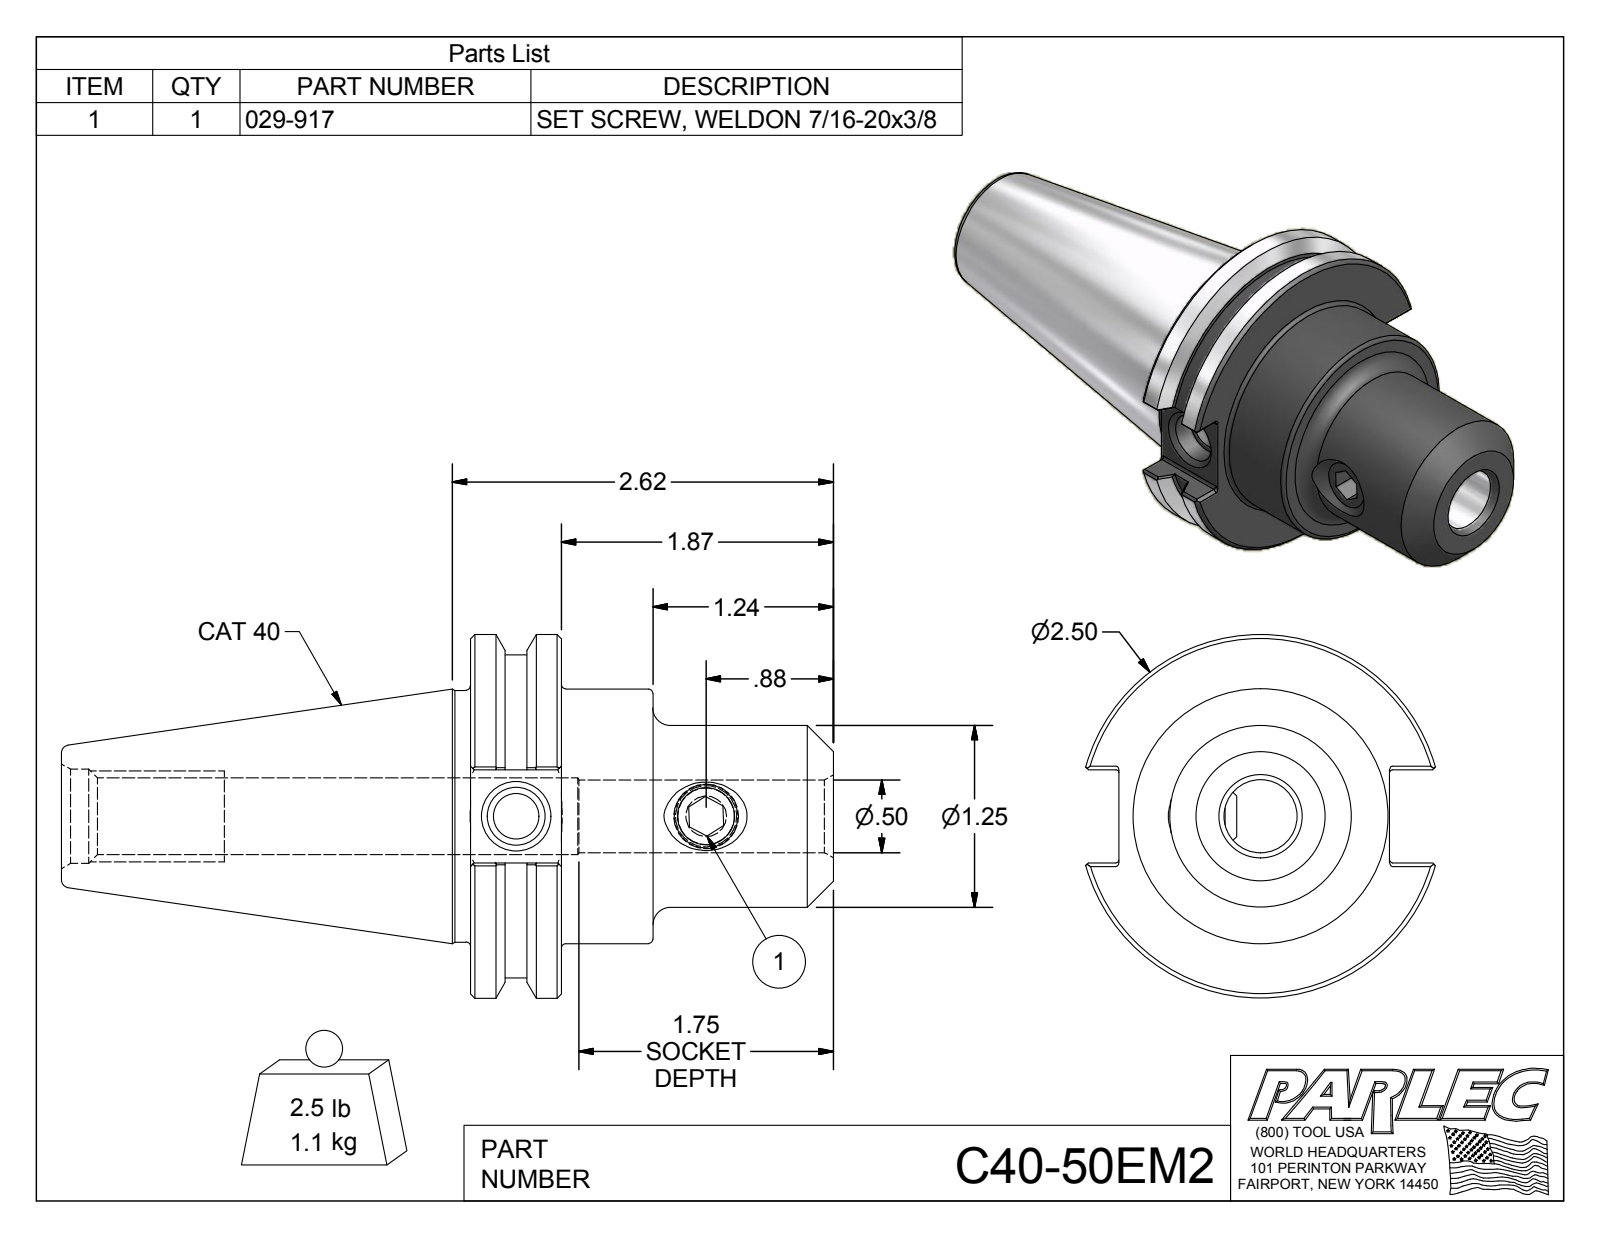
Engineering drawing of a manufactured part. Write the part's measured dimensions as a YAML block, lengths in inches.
part_name: "C40-50EM2; C40-50EM2-1; 029-917"
step_written_by: "Autodesk Inventor 2018 (AUTOMOTIVE_DESIGN)"
units: inches
bodies: {solids: 2, faces: 104, planar: 41, cylindrical: 29, other: 34}
overall_size: [5.307, 2.5, 2.406]
volume: 8.71
surface_area: 43.17
round_holes:
  - {diameter: 0.315, count: 1}
  - {diameter: 0.391, count: 1}
  - {diameter: 0.399, count: 1}
  - {diameter: 0.5, count: 1}
  - {diameter: 0.527, count: 1}
  - {diameter: 0.648, count: 1}
round_bosses_or_shafts:
  - {diameter: 2.5, count: 1}
  - {diameter: 2.219, count: 1}
  - {diameter: 1.75, count: 1}
  - {diameter: 1.73, count: 1}
  - {diameter: 1.25, count: 1}
  - {diameter: 0.437, count: 1}
partial_cylinders:
  - {radius: 0.02, count: 12}
face_to_face_distances: [0.625, 1.255, 0.63, 2.495, 1.87, 1.24, 0.236, 0.64, 1.86, 2.812]
hole_center_spacings: [1.305]
